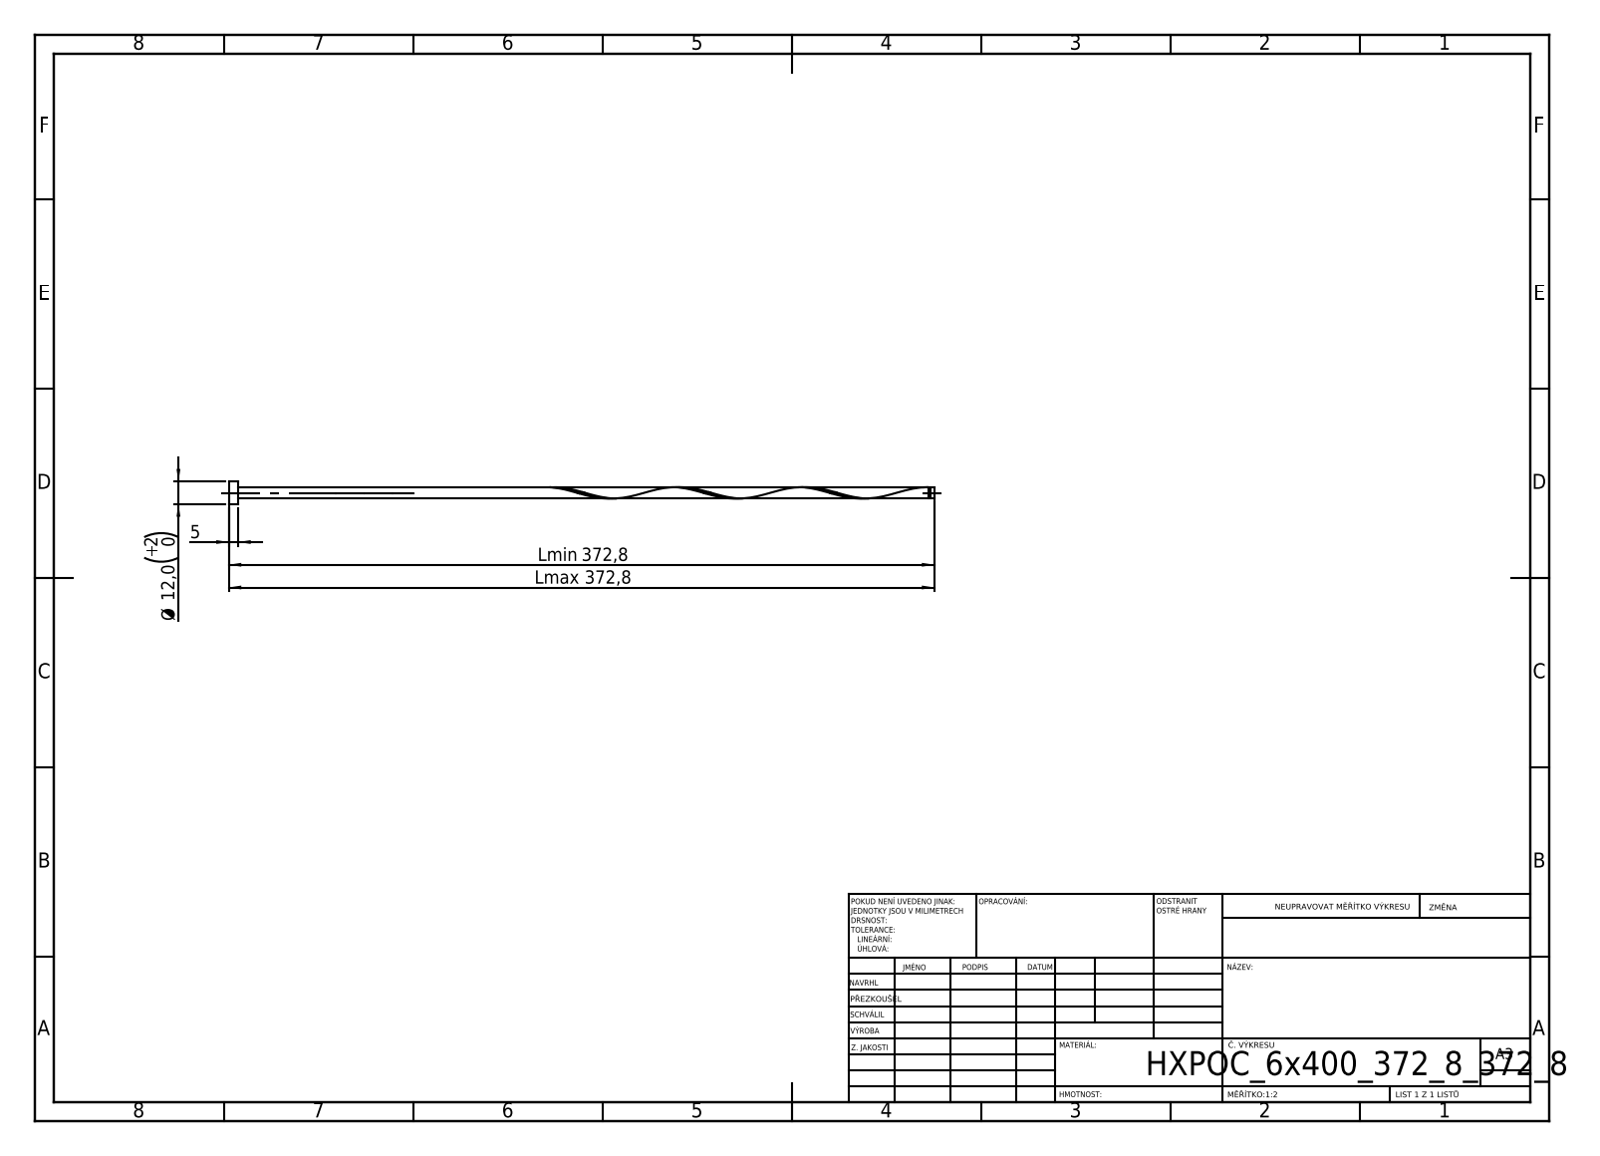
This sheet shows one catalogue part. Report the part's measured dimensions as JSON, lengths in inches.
{"step_written_by": "SolidWorks 2019 (CONFIG_CONTROL_DESIGN)", "units": "inches", "bodies": {"solids": 1, "faces": 16, "planar": 6, "cylindrical": 9, "other": 1}, "overall_size": [14.677, 0.472, 0.472], "volume_in3": 0.815, "surface_area_in2": 15.5, "round_bosses_or_shafts": [[0.472, 1], [0.236, 1], [0.189, 1]], "face_to_face_distances": [0.197, 14.677, 14.48, 14.593, 14.396, 0.084, 14.546, 14.349, 0.047, 0.131]}
